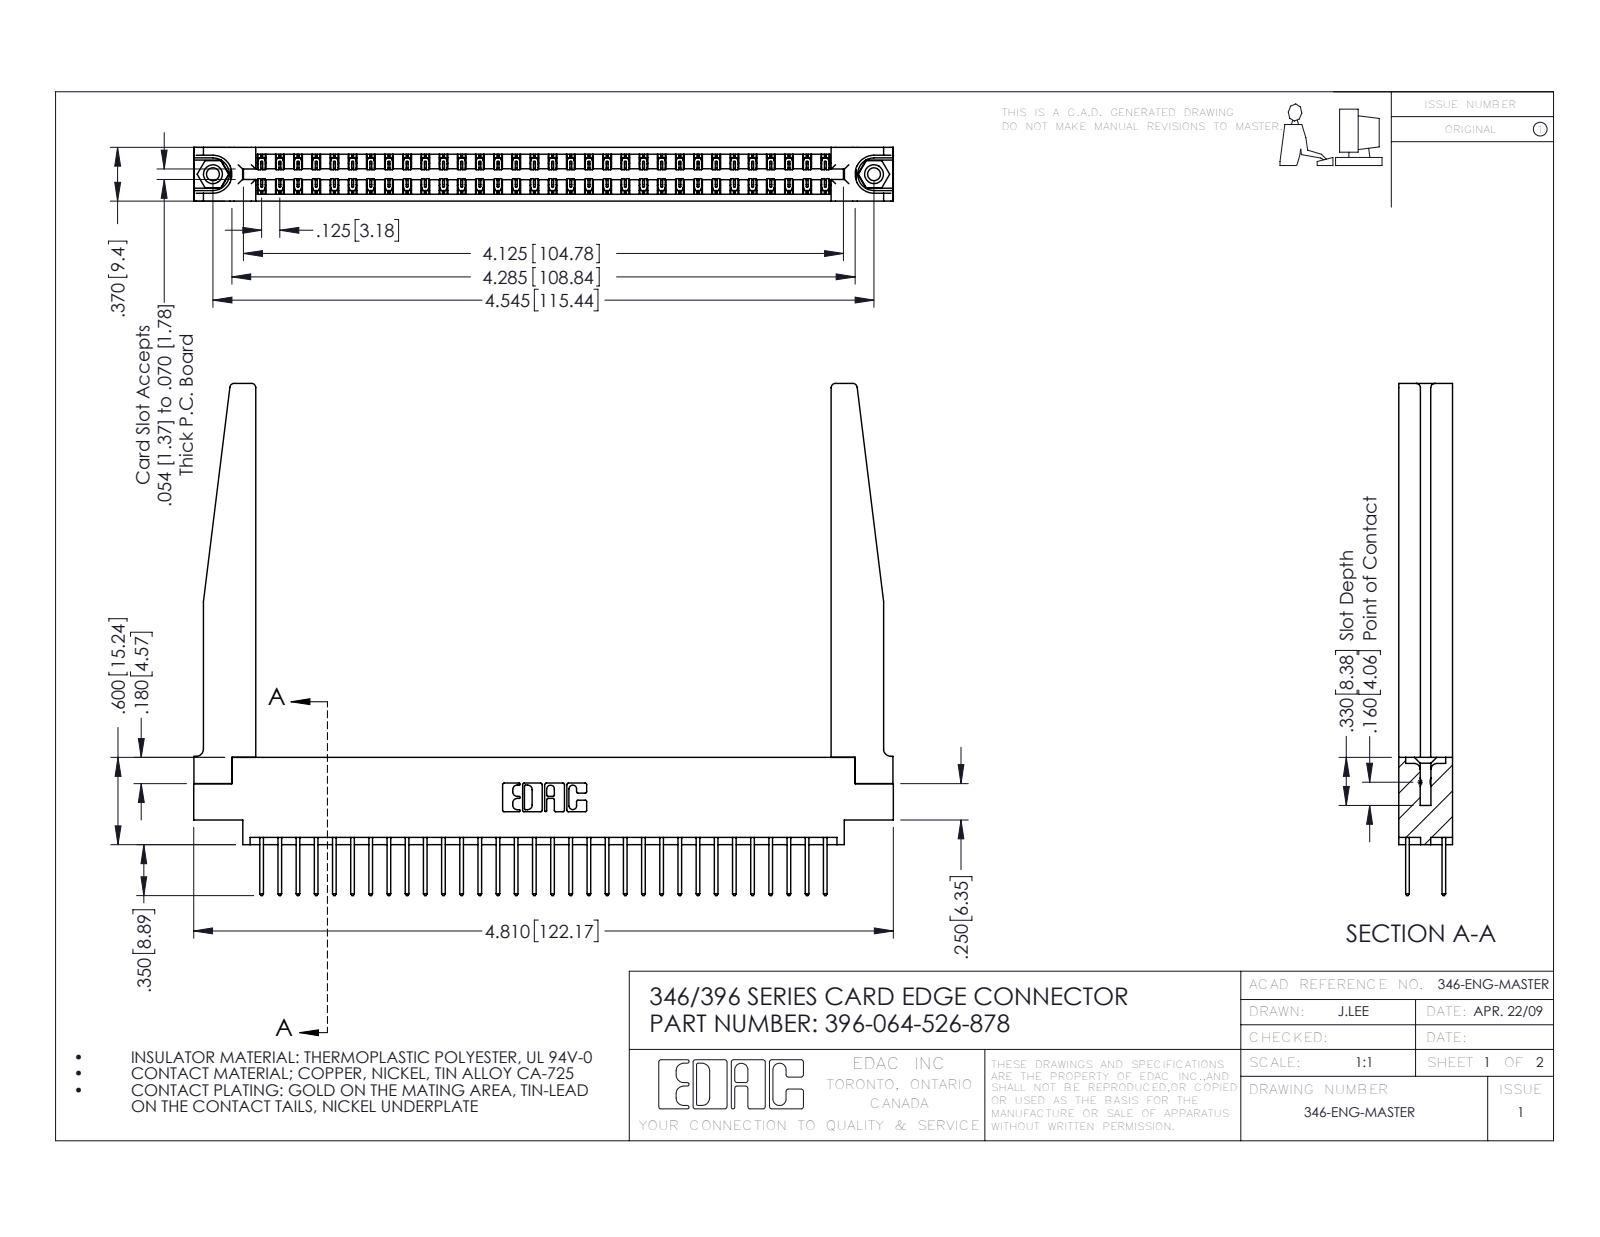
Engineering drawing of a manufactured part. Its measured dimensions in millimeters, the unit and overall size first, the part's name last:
Units: millimetres
Overall size (bounding box): 122.2 × 89.4 × 9.4
Round holes (diameter × count): ⌀2.3 ×2, ⌀3.2 ×2, ⌀4 ×2, ⌀1.6 ×1
Round bosses / shafts (diameter × count): ⌀3.9 ×2
Partial cylindrical surfaces — rounded edges, fillets, slot ends (radius × count): R0.2 ×96, R0.3 ×64, R0.3 ×22, R0.8 ×8, R0.2 ×6, R0.8 ×6, R0.7 ×3, R0.4 ×2
Main face-to-face distances: 9.4, 1.2, 8.2, 1.8, 6.4, 3.8, 3.8, 7.6, 0.6, 7
Hole centre spacings: 6.2, 110.2, 115.4
Volume: 18 700 mm³ · Surface area: 23 230 mm²
Bodies: 69 solids, 3688 faces (2462 planar, 1174 cylindrical, 52 other)
Part name (STEP PRODUCT): 396-064-526-878; 345-292-001_345-293-126; 346 Part_0.170 Offset - 0.156 Dia-TH; 345-250-001_345-250-001-102 (+1 more)
STEP written by: SolidWorks 2016 (CONFIG_CONTROL_DESIGN)
